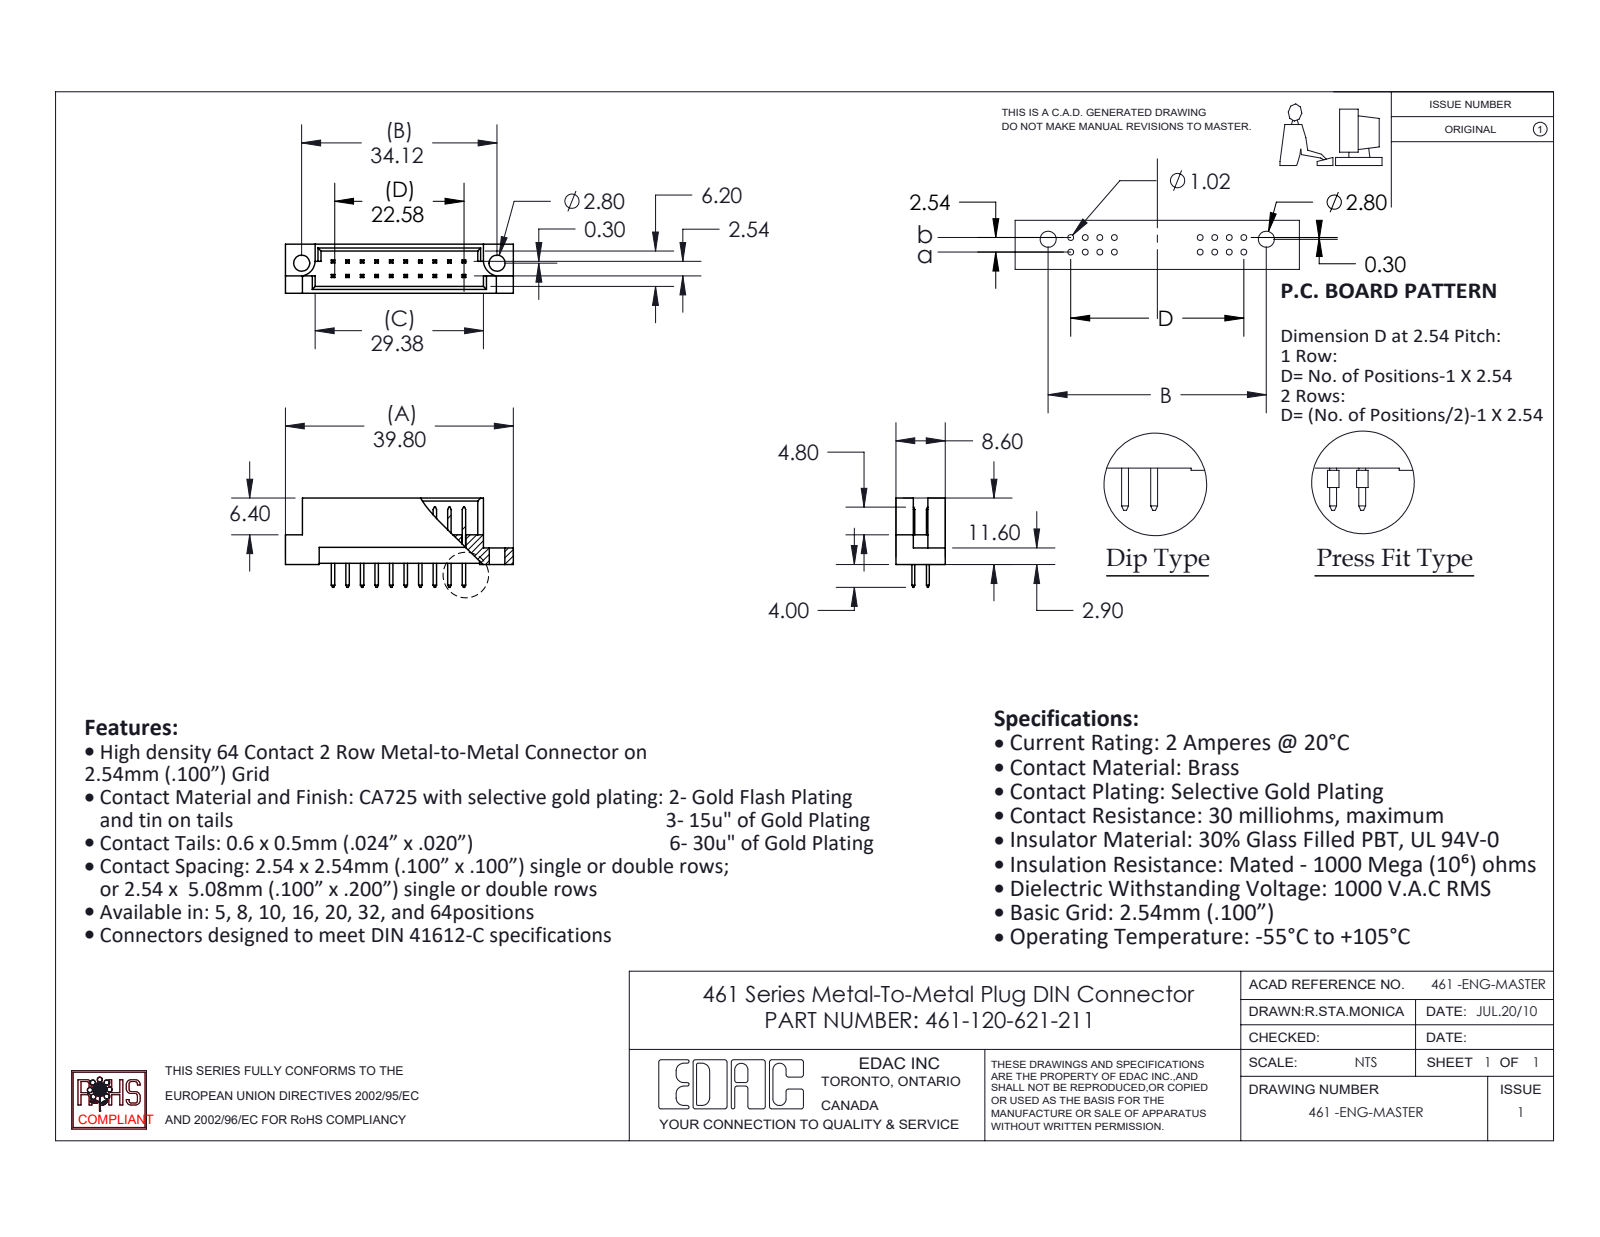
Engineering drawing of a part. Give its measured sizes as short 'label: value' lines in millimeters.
name: 461-290_21; 461 Part_20; 461-120-621-211
written by: SolidWorks 2020 (CONFIG_CONTROL_DESIGN)
unit: mm
bodies: 21 solids, 408 faces (402 planar, 6 cylindrical, 0 other)
size: 39.8 × 15.6 × 8.6
volume: 1 986 mm³; area: 2 946 mm²
holes: 2× ⌀2.8
rounds: 2× R2.8
face distances: 1.2, 7.4, 2.54, 8.6, 6.2, 3.28, 5.32, 2.08, 4.12, 2.78
hole spacings: 34.12
